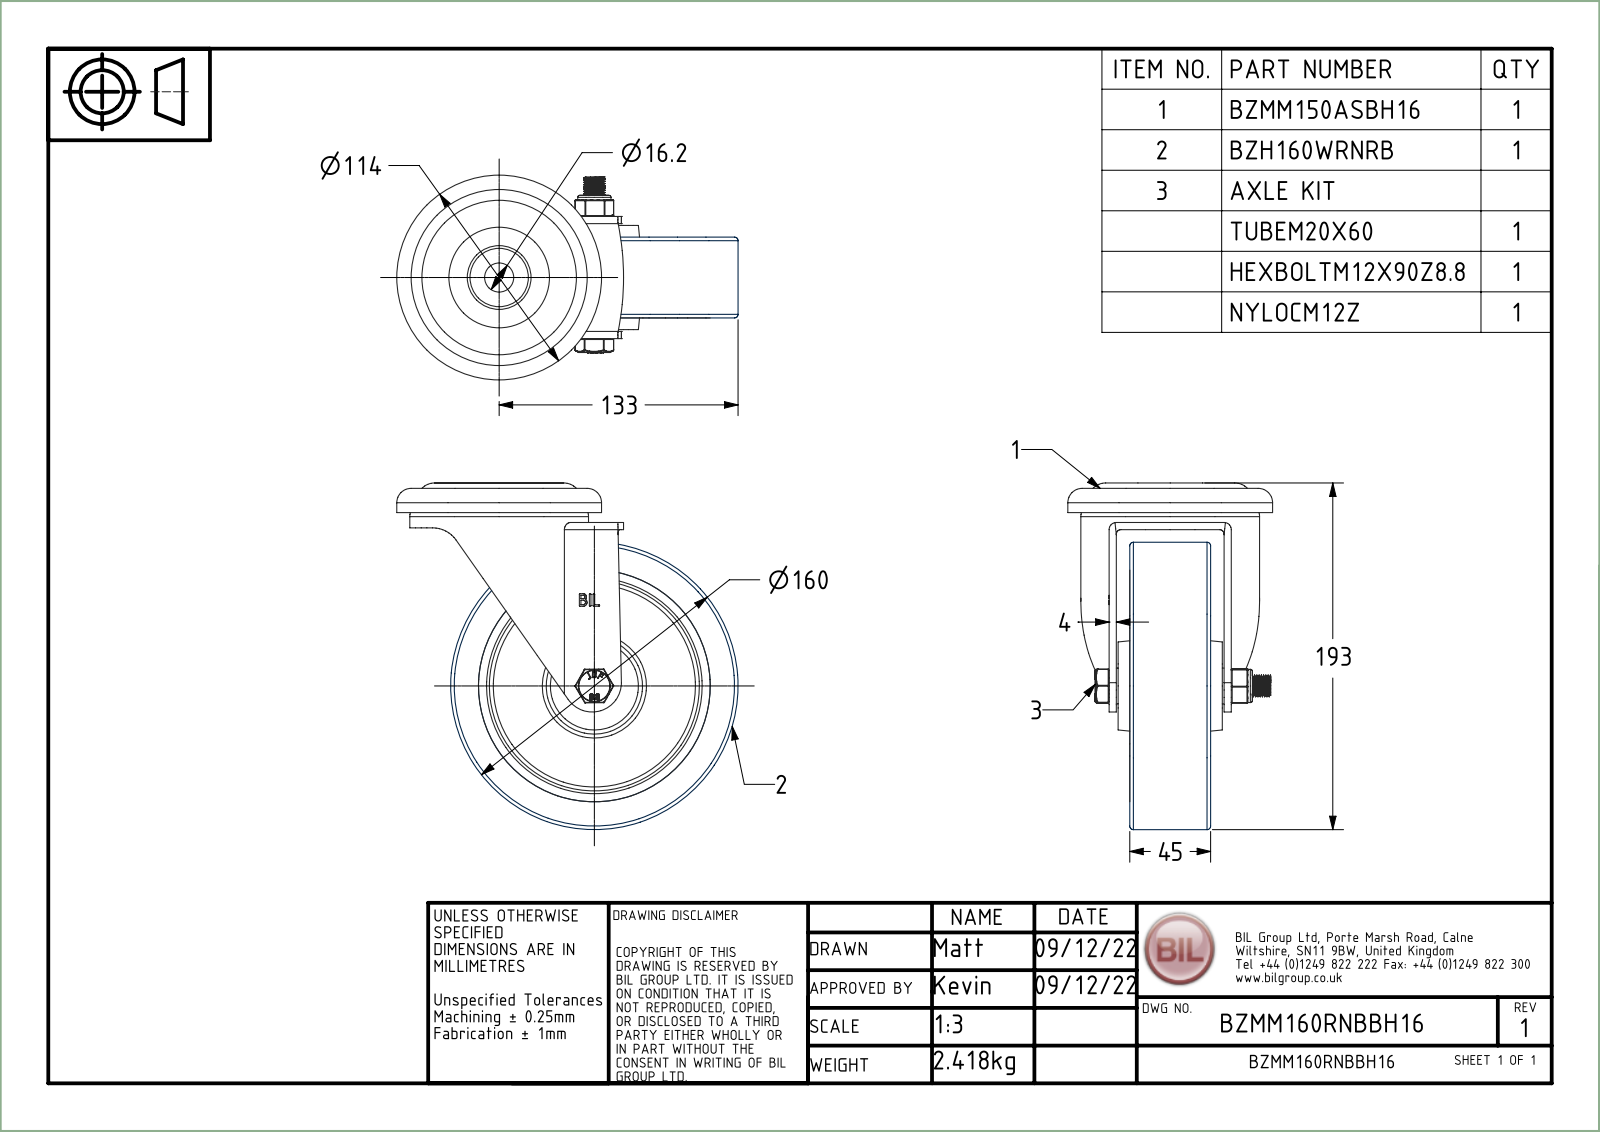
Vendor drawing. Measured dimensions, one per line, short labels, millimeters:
name: BZMM150ASBH16; ZINC PLATED, PRESSED STEEL HEAD; ZINC PLATED, PRESSED STEEL FORKS; BZMM160RNBBH16 (+8 more)
written by: Spatial InterOp 3D (AUTOMOTIVE_DESIGN)
unit: mm
bodies: 20 solids, 658 faces (263 planar, 256 cylindrical, 139 other)
size: 193 × 190 × 114
volume: 791 164 mm³; area: 241 946 mm²
holes: 1× ⌀12, 1× ⌀12.2, 1× ⌀12.5, 1× ⌀14, 1× ⌀16.2, 1× ⌀20, 1× ⌀21, 1× ⌀22, 1× ⌀30, 1× ⌀36.5, 1× ⌀41, 1× ⌀51.5
bosses: 10× ⌀5, 1× ⌀160, 1× ⌀114, 1× ⌀99.5, 1× ⌀74, 1× ⌀47, 1× ⌀32.5, 1× ⌀29.5
rounds: 24× R0.5, 4× R0.47, 4× R0.9, 4× R2.5, 2× R0.89, 2× R0.89, 2× R4, 2× R6.78
face distances: 26.5, 18.5, 8, 45, 26, 4, 52.5, 7.5, 34, 2.75
